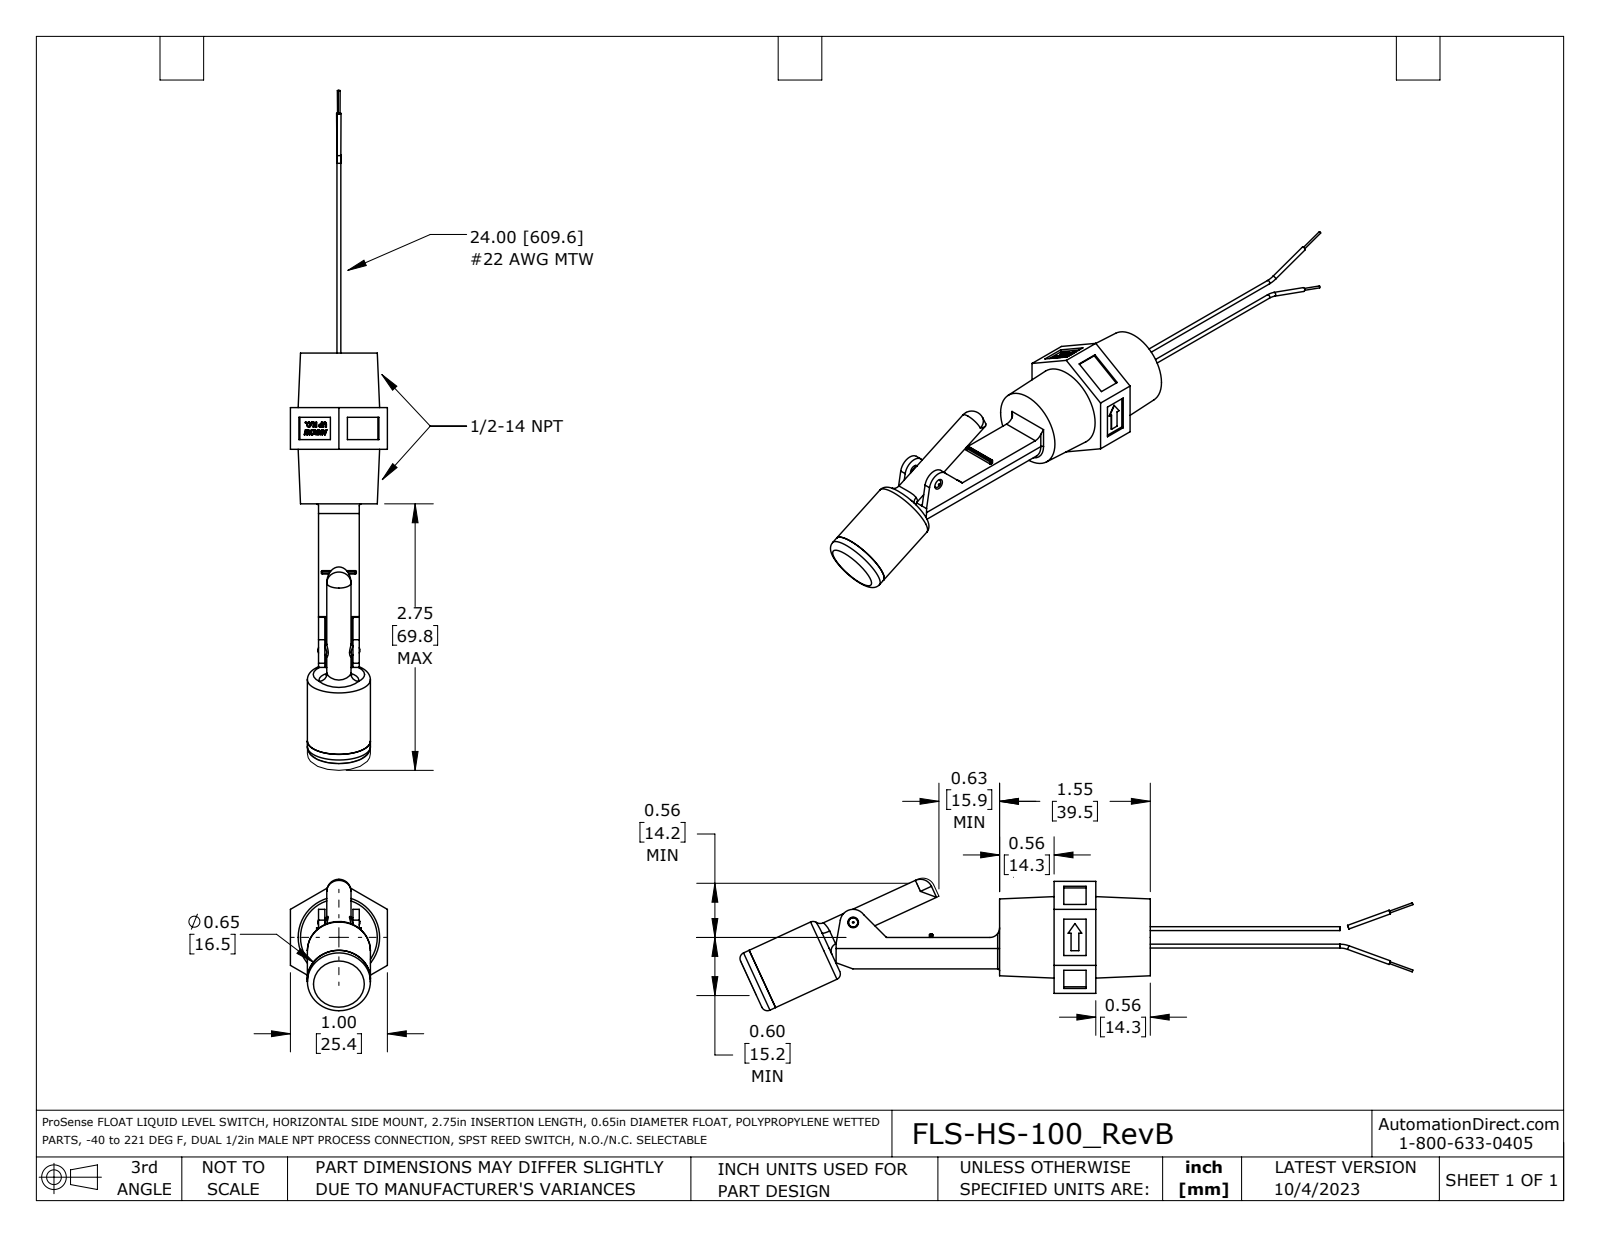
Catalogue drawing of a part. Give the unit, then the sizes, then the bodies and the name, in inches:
Units: inches
Overall size (bounding box): 6.939 × 1.355 × 1
Round holes (diameter × count): ⌀0.01 ×2, ⌀0.53 ×2, ⌀0.11 ×1, ⌀0.45 ×1, ⌀0.5 ×1, ⌀0.56 ×1
Round bosses / shafts (diameter × count): ⌀0.04 ×4, ⌀0.02 ×2, ⌀0.65 ×1, ⌀0.55 ×1, ⌀0.25 ×1, ⌀0.125 ×1
Partial cylindrical surfaces — rounded edges, fillets, slot ends (radius × count): R0.01 ×9, R0.009 ×4, R0.02 ×2, R0.1 ×1, R0.105 ×1, R0.125 ×1, R0.135 ×1, R0.21 ×1
Main face-to-face distances: 0.43, 1, 0.98, 0.02, 0.14, 0.28, 0.29, 0.57, 0.71, 0.562
Hole centre spacings: 0.09, 0.18
Volume: 1.034 in³ · Surface area: 20.28 in²
Bodies: 7 solids, 521 faces (294 planar, 67 cylindrical, 160 other)
Part name (STEP PRODUCT): M8700_FLS-HS-100 nc coord
STEP written by: SolidWorks 2021 (AUTOMOTIVE_DESIGN)
